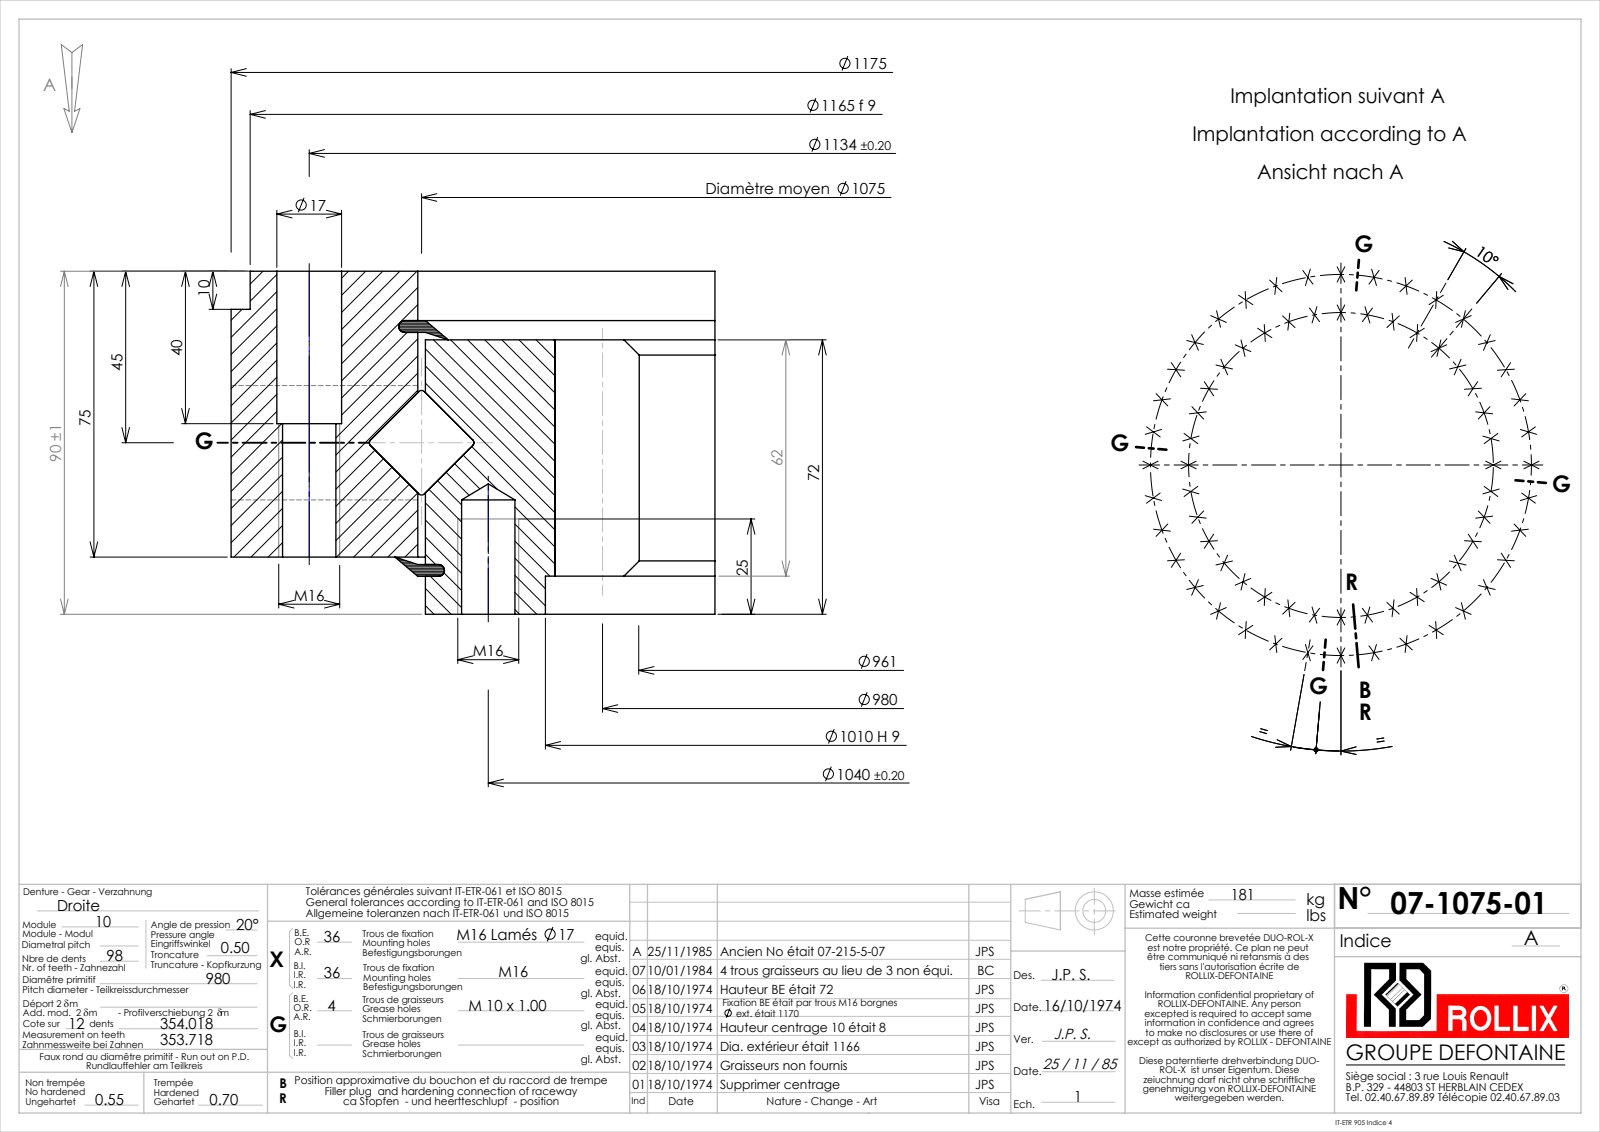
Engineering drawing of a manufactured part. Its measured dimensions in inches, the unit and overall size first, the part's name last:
Units: inches
Overall size (bounding box): 46.26 × 46.26 × 3.543
Round holes (diameter × count): ⌀0.551 ×72, ⌀0.669 ×36, ⌀0.354 ×4, ⌀39.764 ×1, ⌀42.402 ×1
Round bosses / shafts (diameter × count): ⌀46.26 ×1, ⌀45.866 ×1, ⌀42.244 ×1, ⌀0.787 ×1
Partial cylindrical surfaces — rounded edges, fillets, slot ends (radius × count): R18.917 ×1, R19.783 ×1
Main face-to-face distances: 2.953, 2.244, 0.709, 0.591, 2.835, 3.543, 0.077, 2.321, 0.122, 0.199
Hole centre spacings: 20.472, 3.569, 10.597, 14.004, 23.485, 26.319, 28.952, 37.109
Volume: 1 294 in³ · Surface area: 3 599 in²
Bodies: 5 solids, 995 faces (248 planar, 441 cylindrical, 306 other)
Part name (STEP PRODUCT): 07-1075-01
STEP written by: SolidWorks 2016 (CONFIG_CONTROL_DESIGN)
